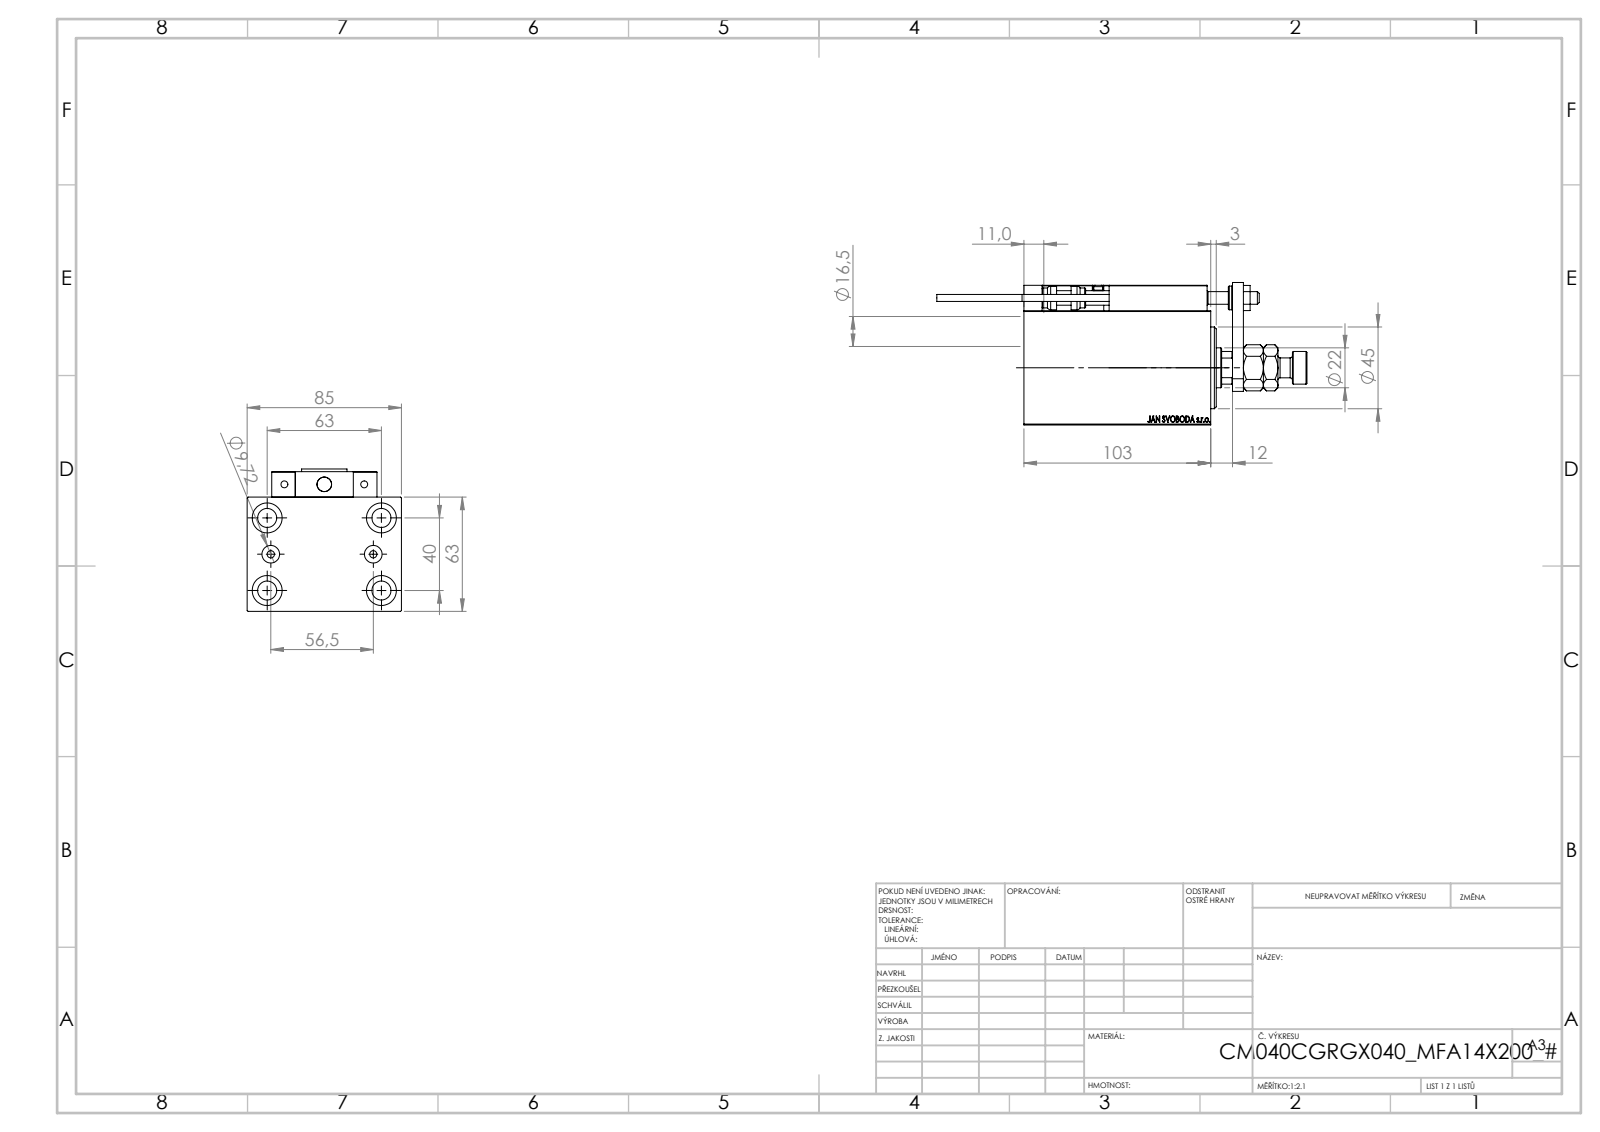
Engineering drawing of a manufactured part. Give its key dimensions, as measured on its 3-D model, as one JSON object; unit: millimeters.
{"part_name": "X_Y_MFA; ZARAZKA; ALLEN BOLT D8; KONCOVKA (+7 more)", "step_written_by": "SolidWorks 2019 (CONFIG_CONTROL_DESIGN)", "units": "millimeters", "bodies": {"solids": 24, "faces": 1330, "planar": 576, "cylindrical": 188, "other": 566}, "overall_size": [204, 85, 78.5], "volume_mm3": 530905, "surface_area_mm2": 109686, "round_holes": [[4, 6], [8, 5], [16.5, 5], [3.2, 4], [10.5, 4], [5, 2], [9.72, 2], [7, 1], [12.5, 1], [22, 1], [25.5, 1], [40, 1]], "round_bosses_or_shafts": [[11, 2], [5, 2], [3.8, 2], [18, 1], [13, 1]], "partial_cylinders_radius": [[0.3, 30], [3, 2], [10.5, 1]], "face_to_face_distances": [63, 85, 14, 103, 18, 10, 65.75, 37.25, 77, 6], "hole_center_spacings": [20.26, 37.31, 63.01, 11.37, 20, 28.25, 29.59, 29.69]}
